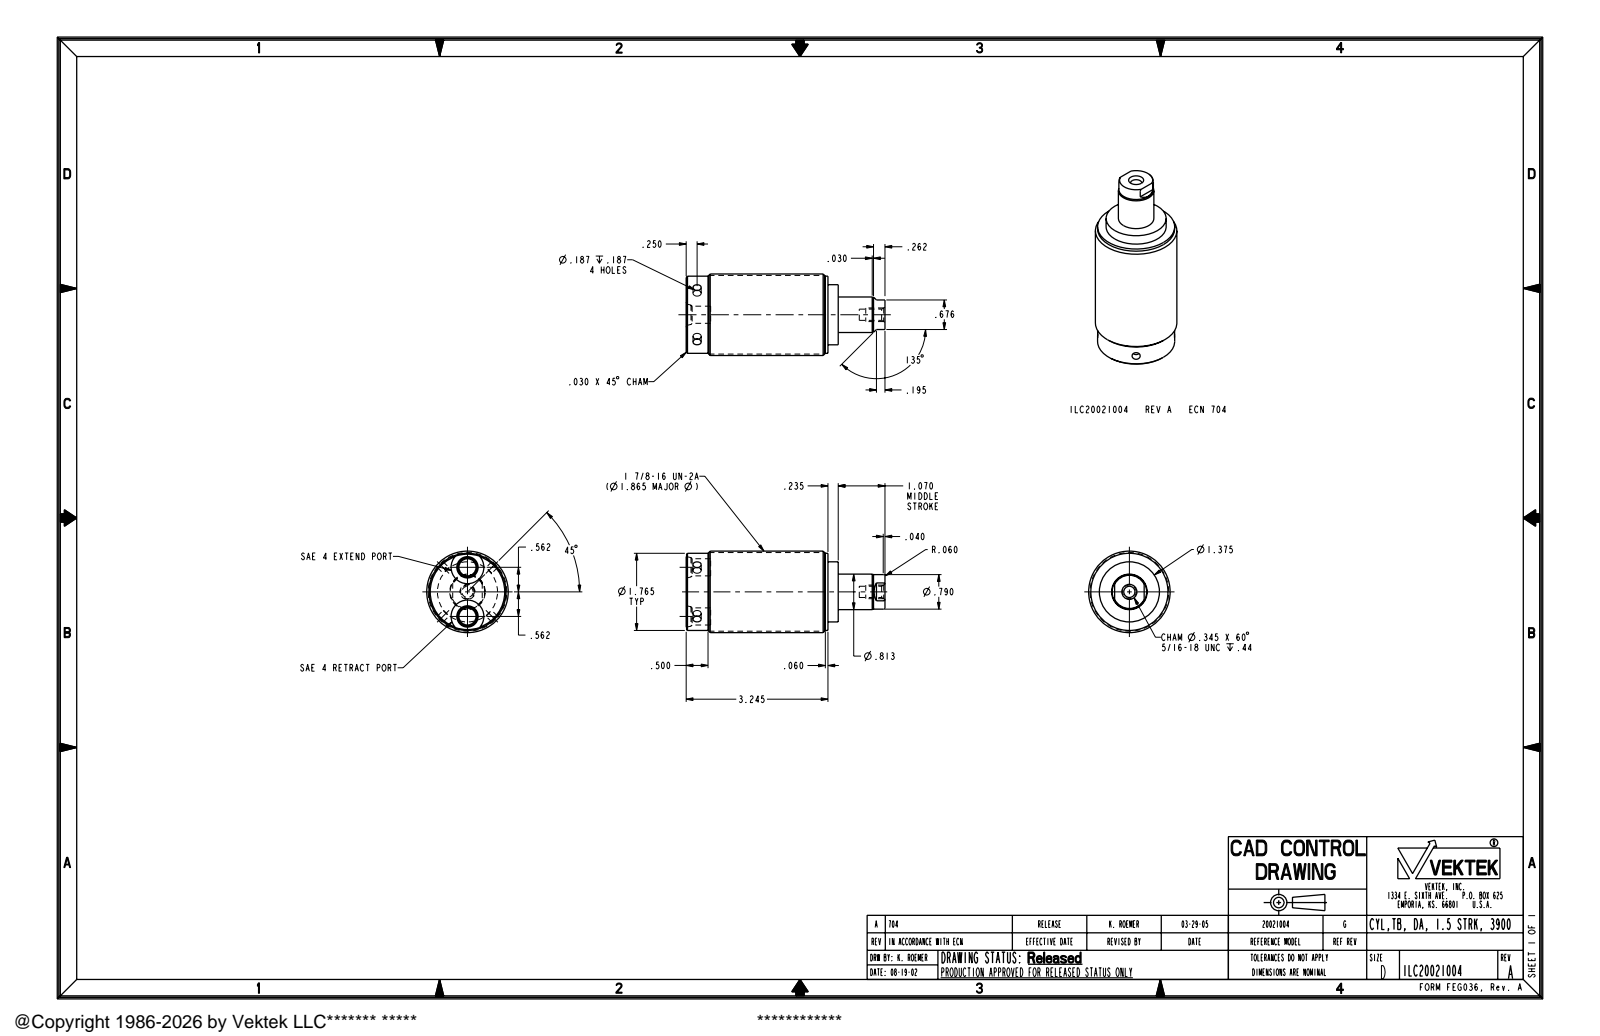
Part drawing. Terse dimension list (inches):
name: ILC20021004
written by: PRO/ENGINEER BY PARAMETRIC TECHNOLOGY CORPORATION, 2004290 (AUTOMOTIVE_DESIGN_CC2)
unit: in
bodies: 1 solid, 70 faces (18 planar, 32 cylindrical, 20 other)
size: 4.55 × 1.865 × 1.865
volume: 9.373 in³; area: 45.15 in²
holes: 2× ⌀0.187, 2× ⌀0.392, 1× ⌀0.257
bosses: 1× ⌀1.865, 1× ⌀1.799, 1× ⌀1.765, 1× ⌀1.375, 1× ⌀0.813, 1× ⌀0.79, 1× ⌀0.312
rounds: 2× R0.375
face distances: 3.48, 0.235, 3.245, 3.47, 3.235, 1.07, 1.305, 4.54, 4.55, 3.99
hole spacings: 0.562, 1.124
